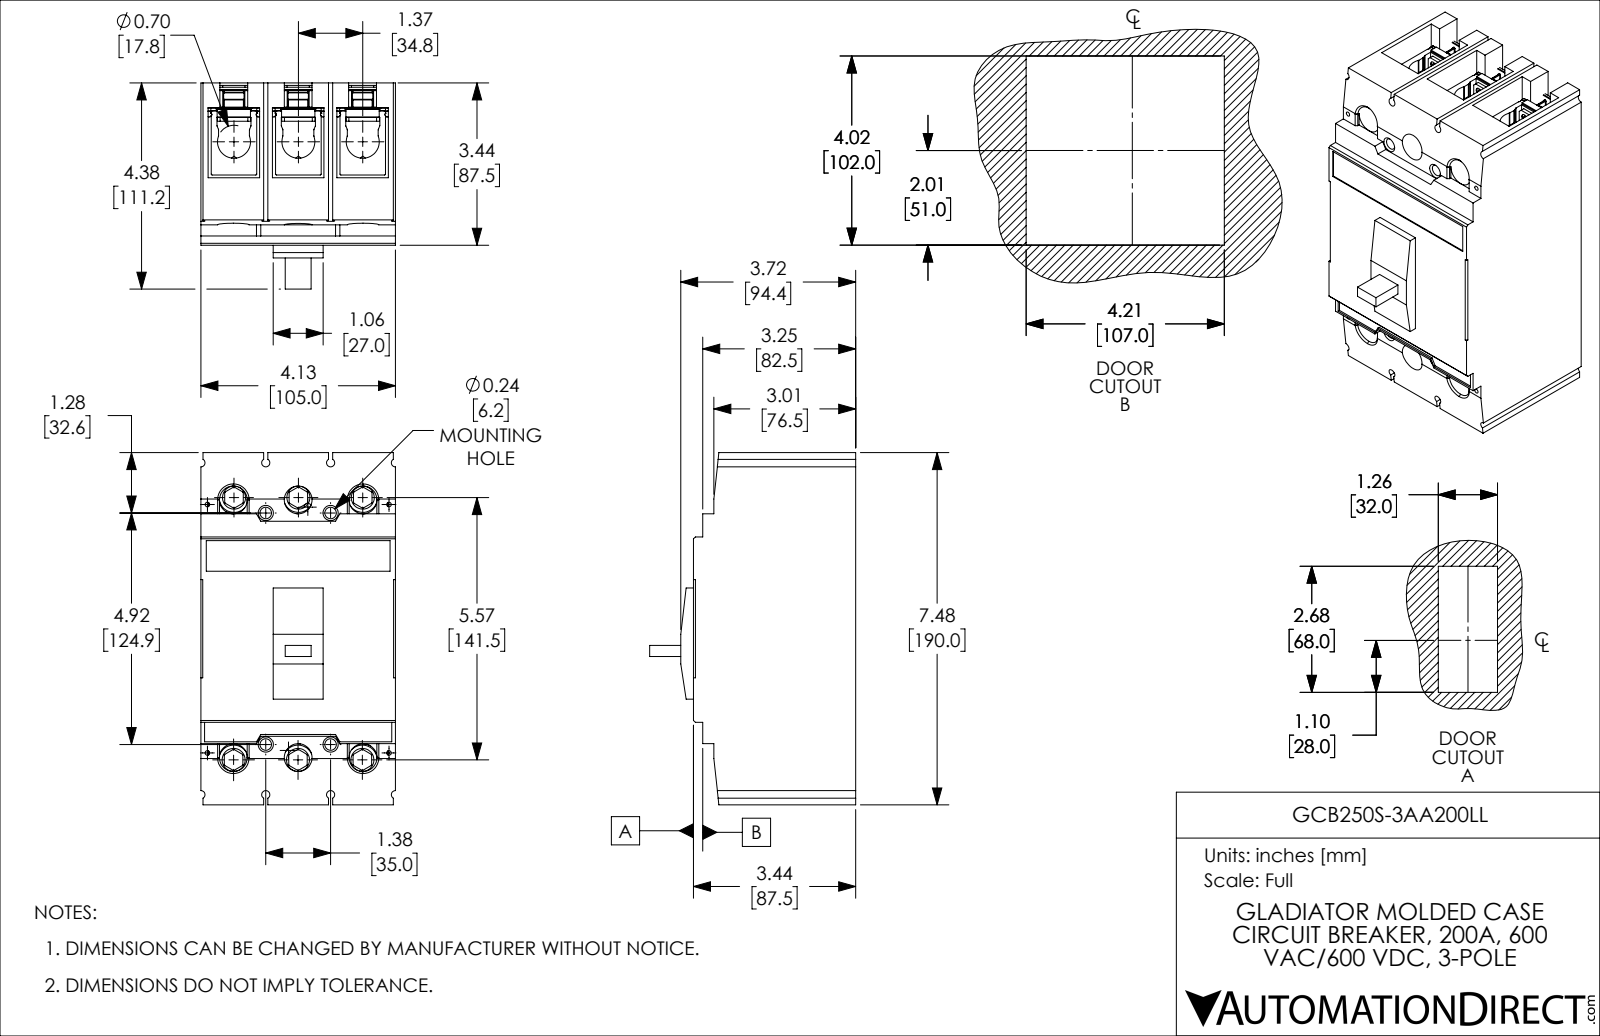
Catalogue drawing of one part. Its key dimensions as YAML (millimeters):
part_name: "GCB250S-3AA200LL"
step_written_by: "SolidWorks 2021 (CONFIG_CONTROL_DESIGN)"
units: millimeters
bodies: {solids: 25, faces: 2233, planar: 975, cylindrical: 958, other: 300}
overall_size: [190, 111.2, 105]
volume: 1427000
surface_area: 203700
round_holes:
  - {diameter: 1.7, count: 24}
  - {diameter: 4, count: 24}
  - {diameter: 2.5, count: 10}
  - {diameter: 9, count: 6}
  - {diameter: 15, count: 6}
  - {diameter: 17.5, count: 6}
  - {diameter: 4.4, count: 4}
  - {diameter: 6.2, count: 4}
round_bosses_or_shafts:
  - {diameter: 18, count: 6}
partial_cylinders:
  - {radius: 0.3, count: 206}
  - {radius: 1, count: 72}
  - {radius: 1.5, count: 36}
  - {radius: 0.5, count: 26}
  - {radius: 0.2, count: 24}
  - {radius: 2, count: 20}
  - {radius: 0.4, count: 12}
  - {radius: 0.8, count: 12}
face_to_face_distances: [34.7, 105, 69.5, 27.8, 21.4, 6.4, 1.5, 35, 155, 87.5]
hole_center_spacings: [7.2, 18.9, 26.6, 35, 133.1, 160, 34.7, 36.2]
